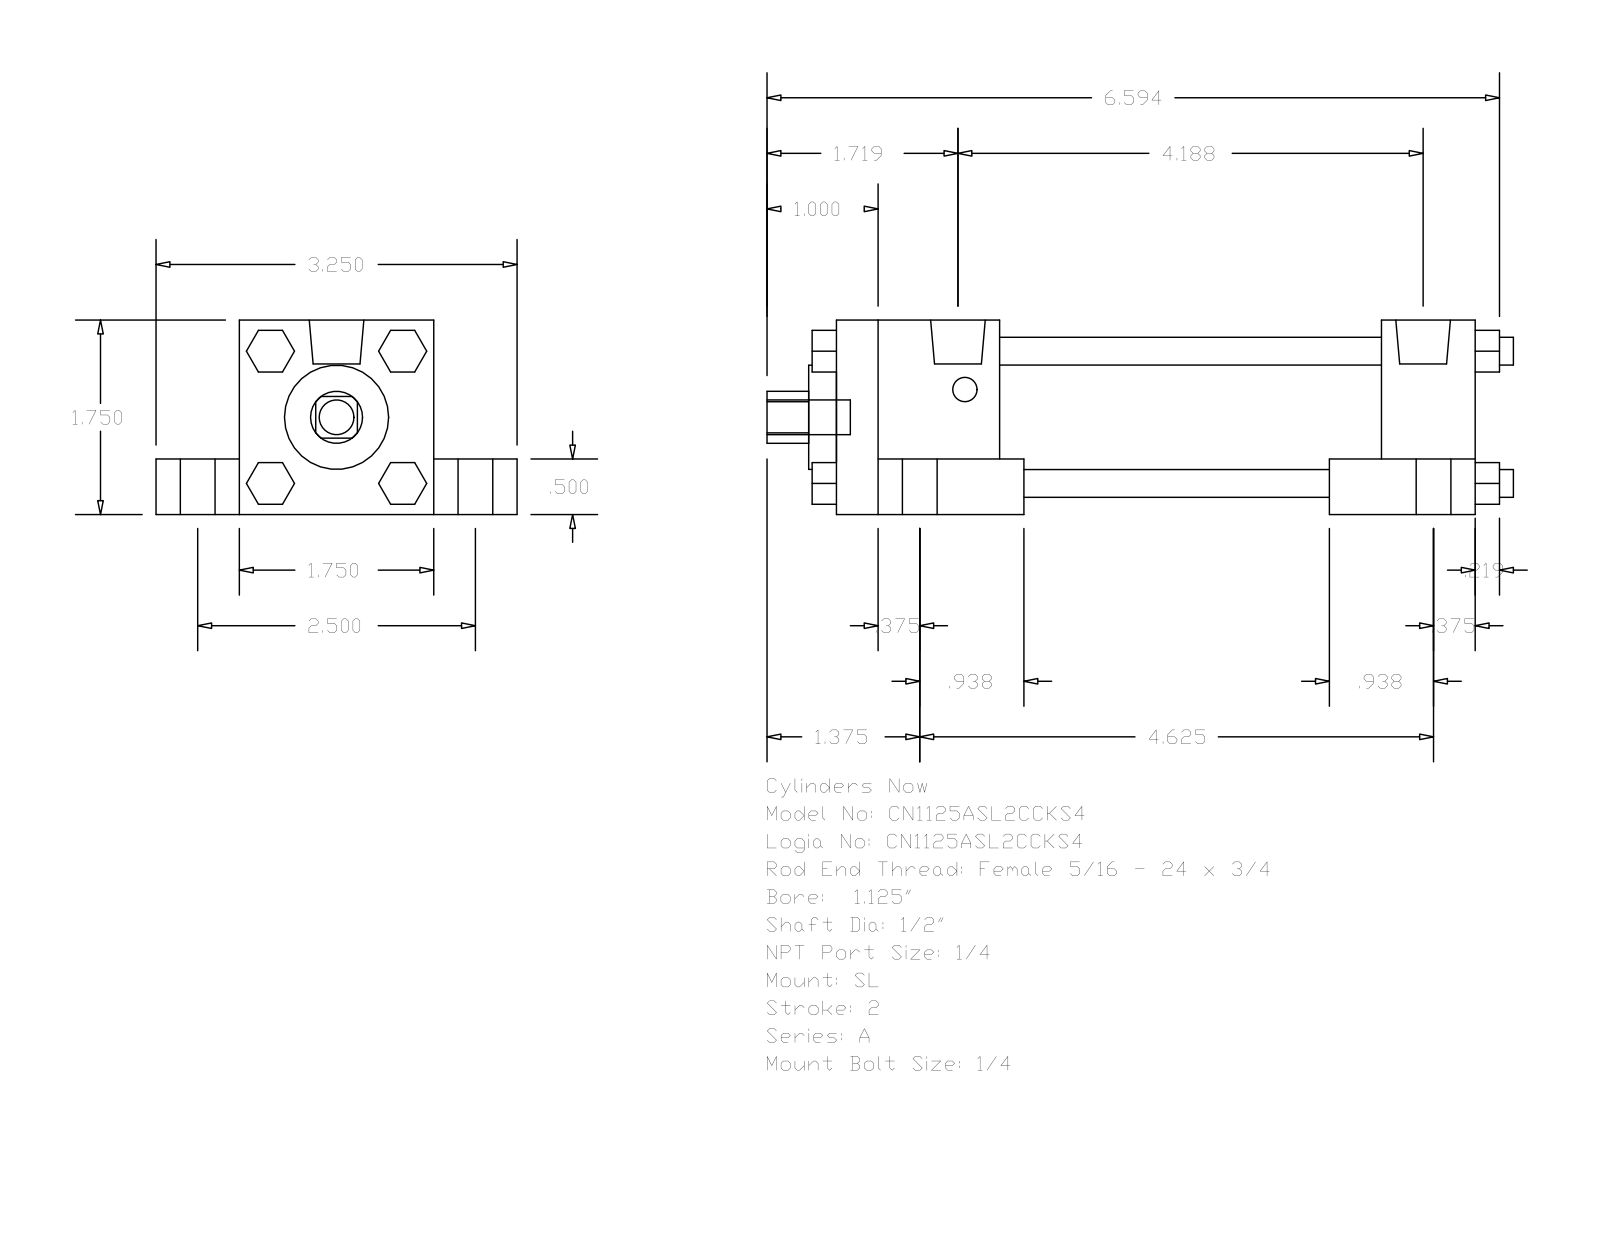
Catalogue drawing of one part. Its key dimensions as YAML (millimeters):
part_name: "A_SL__0112_0.5"
step_written_by: "GSSL Pune (CONFIG_CONTROL_DESIGN)"
units: millimeters
bodies: {solids: 0, faces: 150, planar: 114, cylindrical: 36, other: 0}
overall_size: [170.66, 82.55, 44.45]
round_holes:
  - {diameter: 12.7, count: 1}
  - {diameter: 23.81, count: 1}
  - {diameter: 31.88, count: 1}
round_bosses_or_shafts:
  - {diameter: 7.94, count: 5}
  - {diameter: 14.29, count: 4}
  - {diameter: 6.35, count: 4}
  - {diameter: 5.56, count: 4}
  - {diameter: 12.49, count: 2}
partial_cylinders:
  - {radius: 5.94, count: 1}
face_to_face_distances: [44.46, 31.76, 12.7, 19.04, 63.5, 146.05, 124.61, 21.44, 37.3, 87.31]
